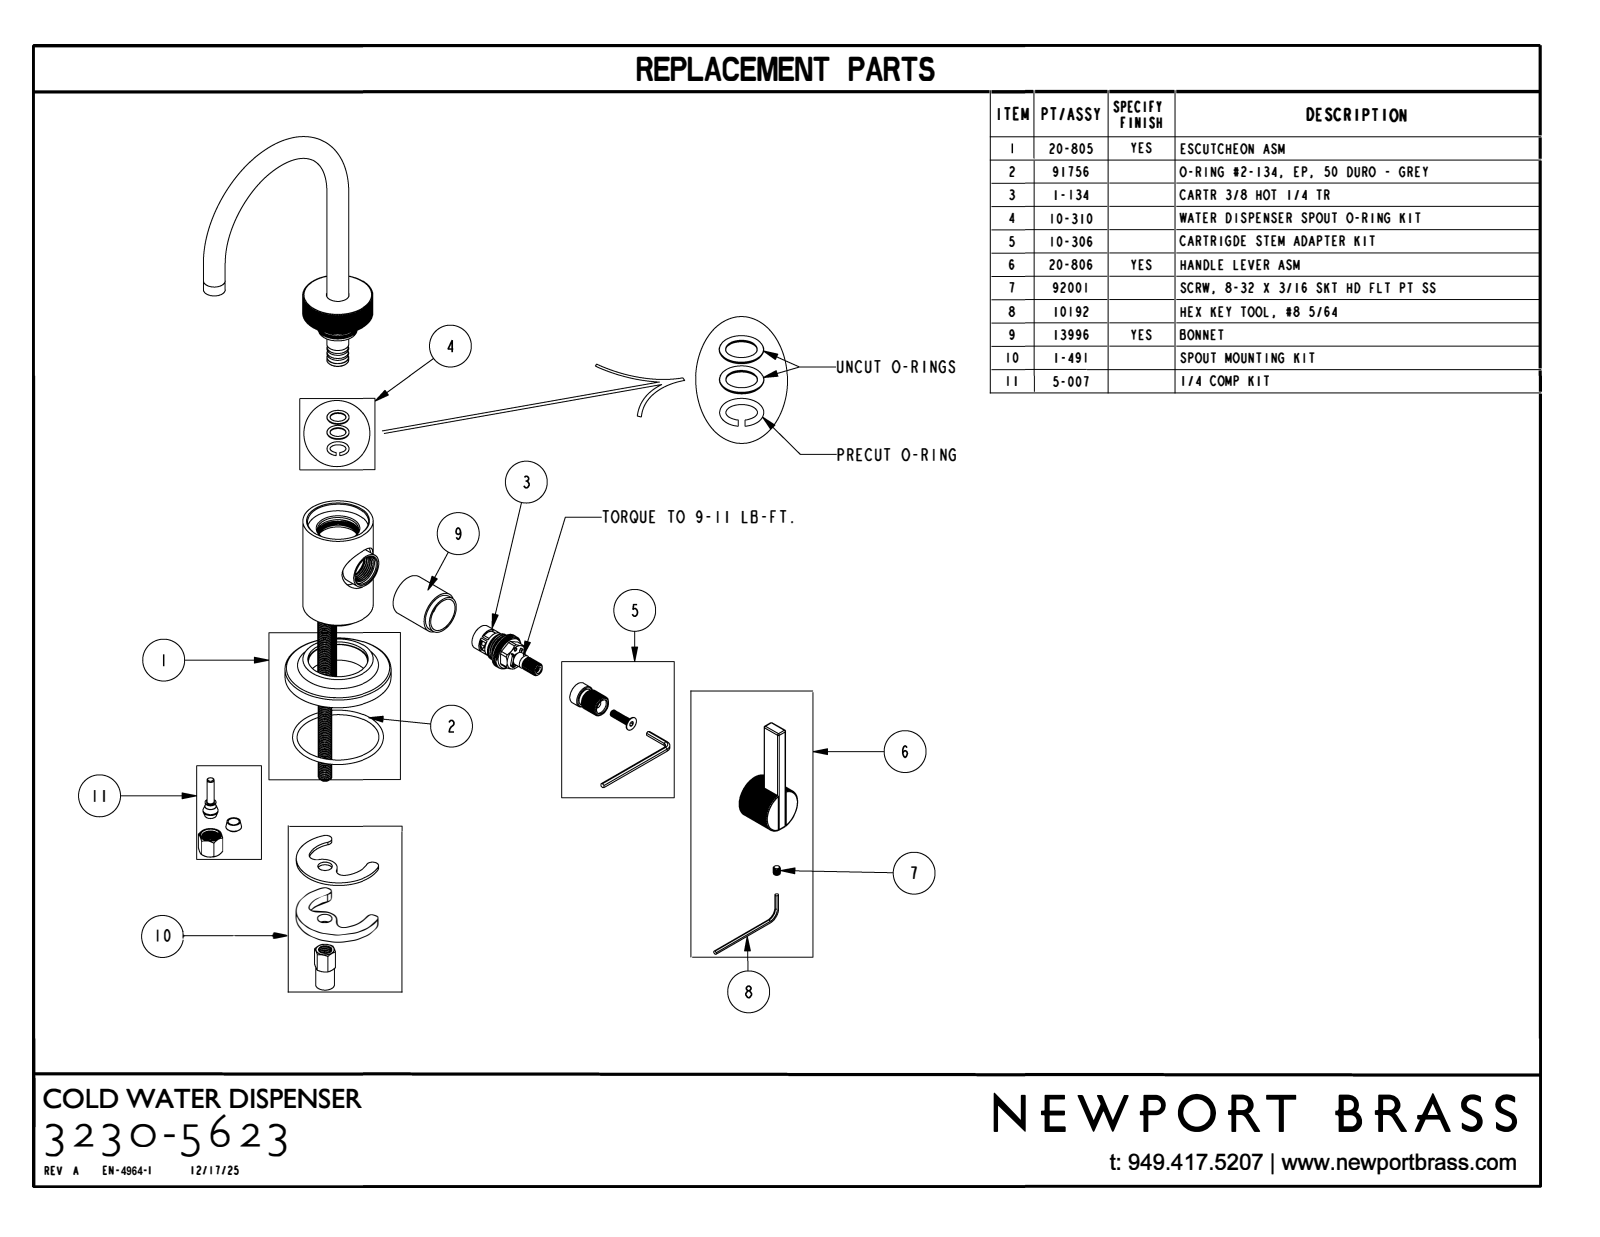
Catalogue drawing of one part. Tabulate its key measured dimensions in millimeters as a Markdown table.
| quantity | value |
| --- | --- |
| part name | 3230-5623 |
| STEP written by | CREO PARAMETRIC BY PTC INC, 2023134 (CONFIG_CONTROL_DESIGN) |
| units | millimeters |
| bodies | 2 solids, 720 faces (414 planar, 250 cylindrical, 56 other) |
| overall size | 238.8 × 138.8 × 94.4 |
| volume | 161 300 mm³ |
| surface area | 47 470 mm² |
| round holes (diameter × count) | 1.7 × 4, 10.2 × 2, 5.1 × 1, 6.4 × 1, 9.4 × 1, 13 × 1, 13.2 × 1, 15.6 × 1, 25.4 × 1 |
| round bosses / shafts (diameter × count) | 12.7 × 2, 61.7 × 1, 40.9 × 1, 24.6 × 1, 9.7 × 1 |
| partial cylindrical surfaces (radius × count) | 0.8 × 12, 1.5 × 2, 13.1 × 1 |
| main face-to-face distances | 85.9, 6.5, 6.4, 23.8, 0.9, 22.9, 18, 18.1, 11.6, 10.7 |
| hole center spacings | 4.7, 6.7, 9.4, 101.7, 96.9, 101.6, 106.3 |
